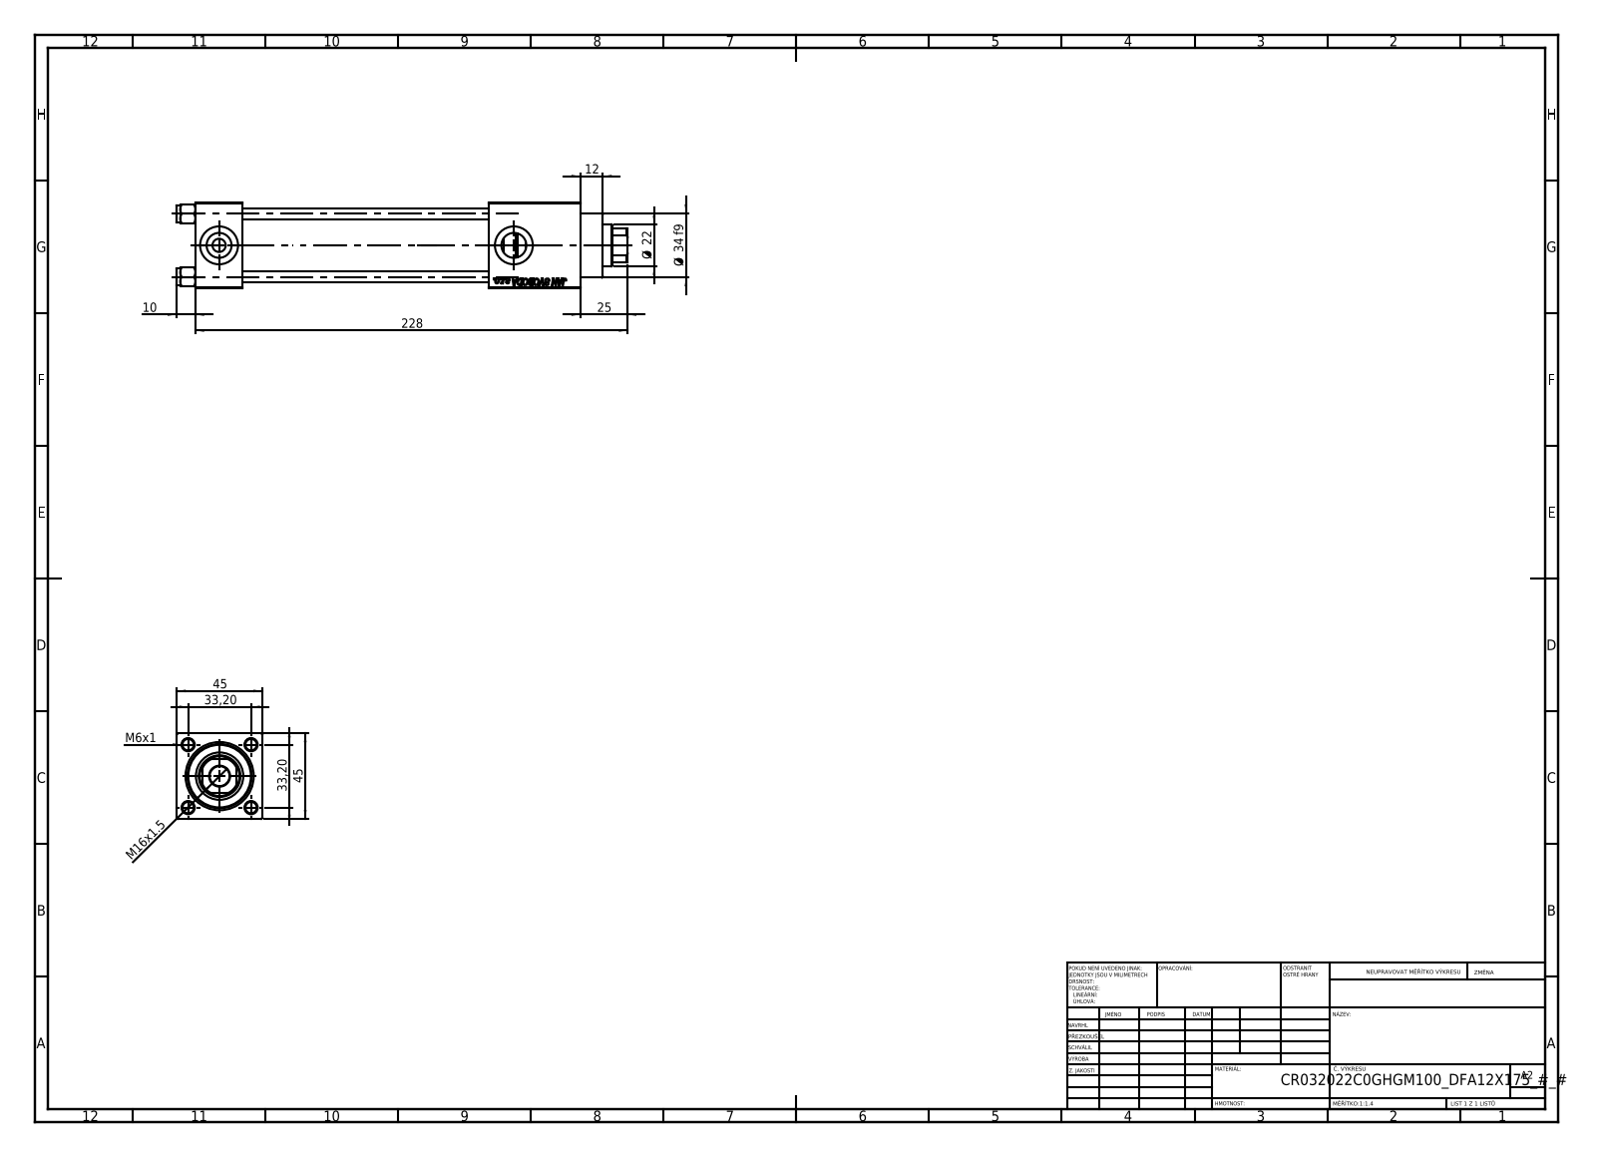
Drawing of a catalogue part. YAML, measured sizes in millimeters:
part_name: "FEMALE_PART_FOR_DFA; V215CR_C_TYCINKA; V215CR_VCP_C; V215_VC_A (+2 more)"
step_written_by: "SolidWorks 2019 (CONFIG_CONTROL_DESIGN)"
units: millimeters
bodies: {solids: 12, faces: 1180, planar: 537, cylindrical: 95, other: 548}
overall_size: [238, 45, 45]
volume: 285519
surface_area: 104880
round_holes:
  - {diameter: 6, count: 4}
  - {diameter: 7, count: 2}
  - {diameter: 13.16, count: 2}
  - {diameter: 20, count: 2}
  - {diameter: 10.5, count: 1}
  - {diameter: 22, count: 1}
  - {diameter: 24, count: 1}
  - {diameter: 25, count: 1}
  - {diameter: 32, count: 1}
  - {diameter: 33, count: 1}
round_bosses_or_shafts:
  - {diameter: 9, count: 4}
  - {diameter: 38, count: 1}
  - {diameter: 34, count: 1}
  - {diameter: 28, count: 1}
  - {diameter: 12, count: 1}
  - {diameter: 10, count: 1}
partial_cylinders:
  - {radius: 9.75, count: 1}
  - {radius: 10.5, count: 1}
face_to_face_distances: [45, 25, 203, 178, 155, 130, 48, 174.3, 149.3, 19.3]
hole_center_spacings: [23.48, 33.2, 46.95, 155.5]
